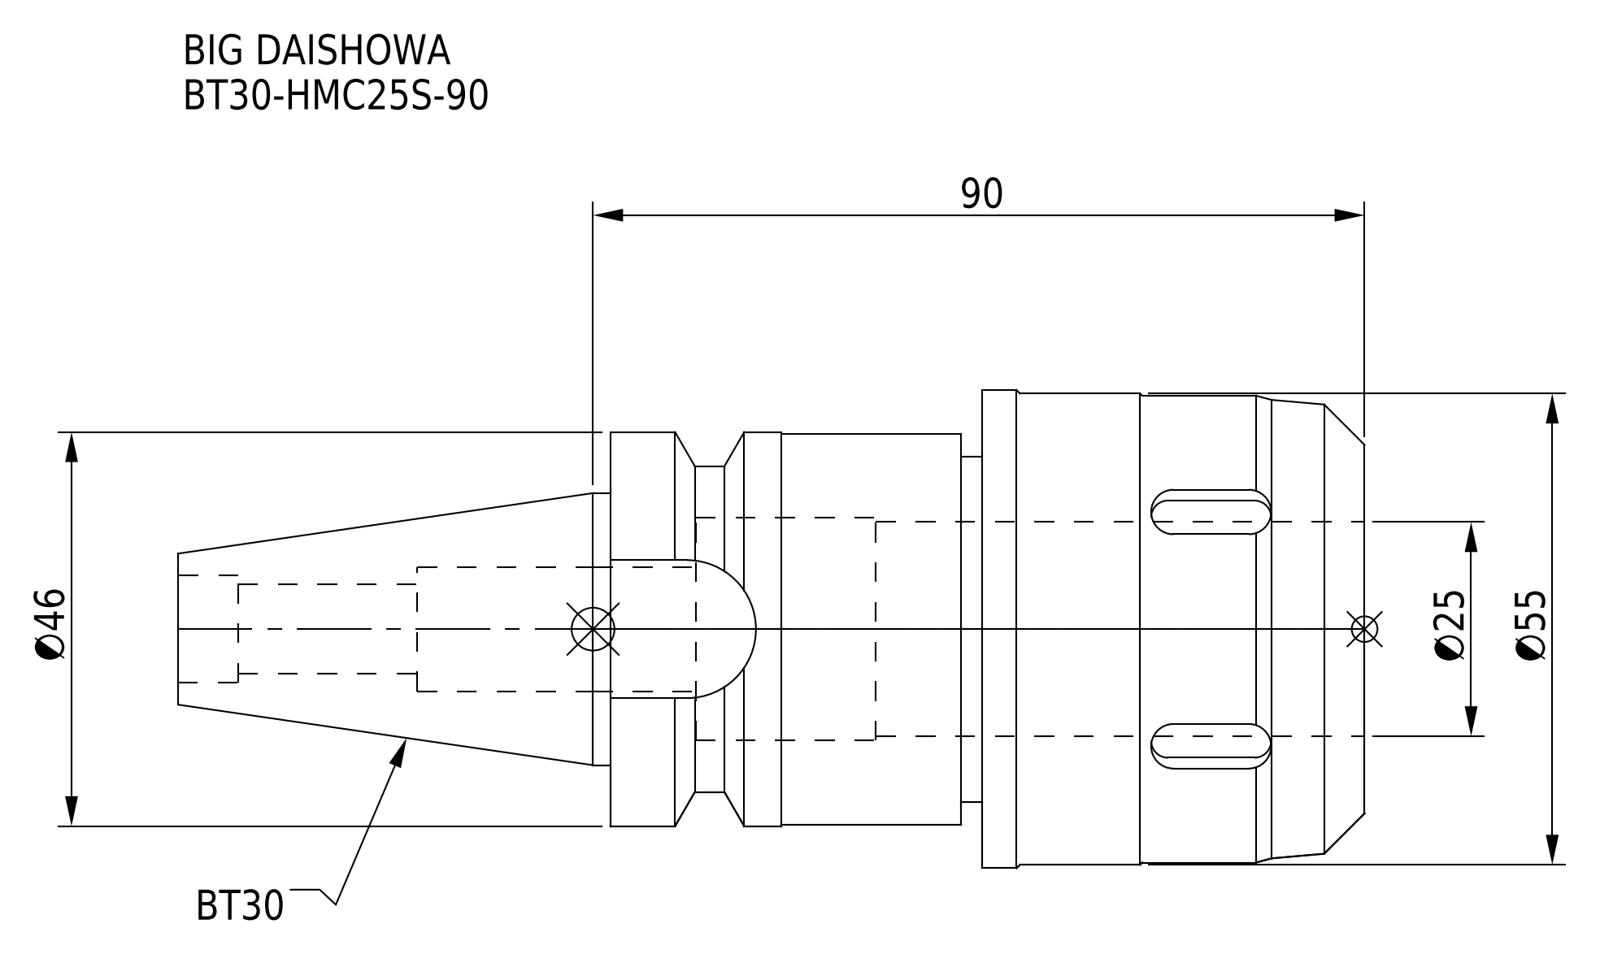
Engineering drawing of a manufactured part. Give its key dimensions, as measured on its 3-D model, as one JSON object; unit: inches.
{"part_name": "BT30-HMC25S-90", "step_written_by": "CREO PARAMETRIC BY PTC INC, 2016380 (AUTOMOTIVE_DESIGN)", "units": "inches", "bodies": {"solids": 1, "faces": 94, "planar": 34, "cylindrical": 44, "other": 16}, "overall_size": [5.449, 2.197, 2.197], "volume_in3": 8.792, "surface_area_in2": 49.12, "round_holes": [[0.409, 1], [0.492, 1], [0.571, 1], [0.984, 1], [1.024, 1]], "round_bosses_or_shafts": [[2.197, 1], [2.165, 1], [2.146, 1], [1.811, 1], [1.795, 1], [1.587, 1], [1.25, 1]], "partial_cylinders_radius": [[0.118, 6], [0.317, 1], [0.748, 1]], "face_to_face_distances": [1.756, 1.709, 3.465, 0.394, 3.071, 1.315, 1.854, 0.098, 1.217, 1.61]}
